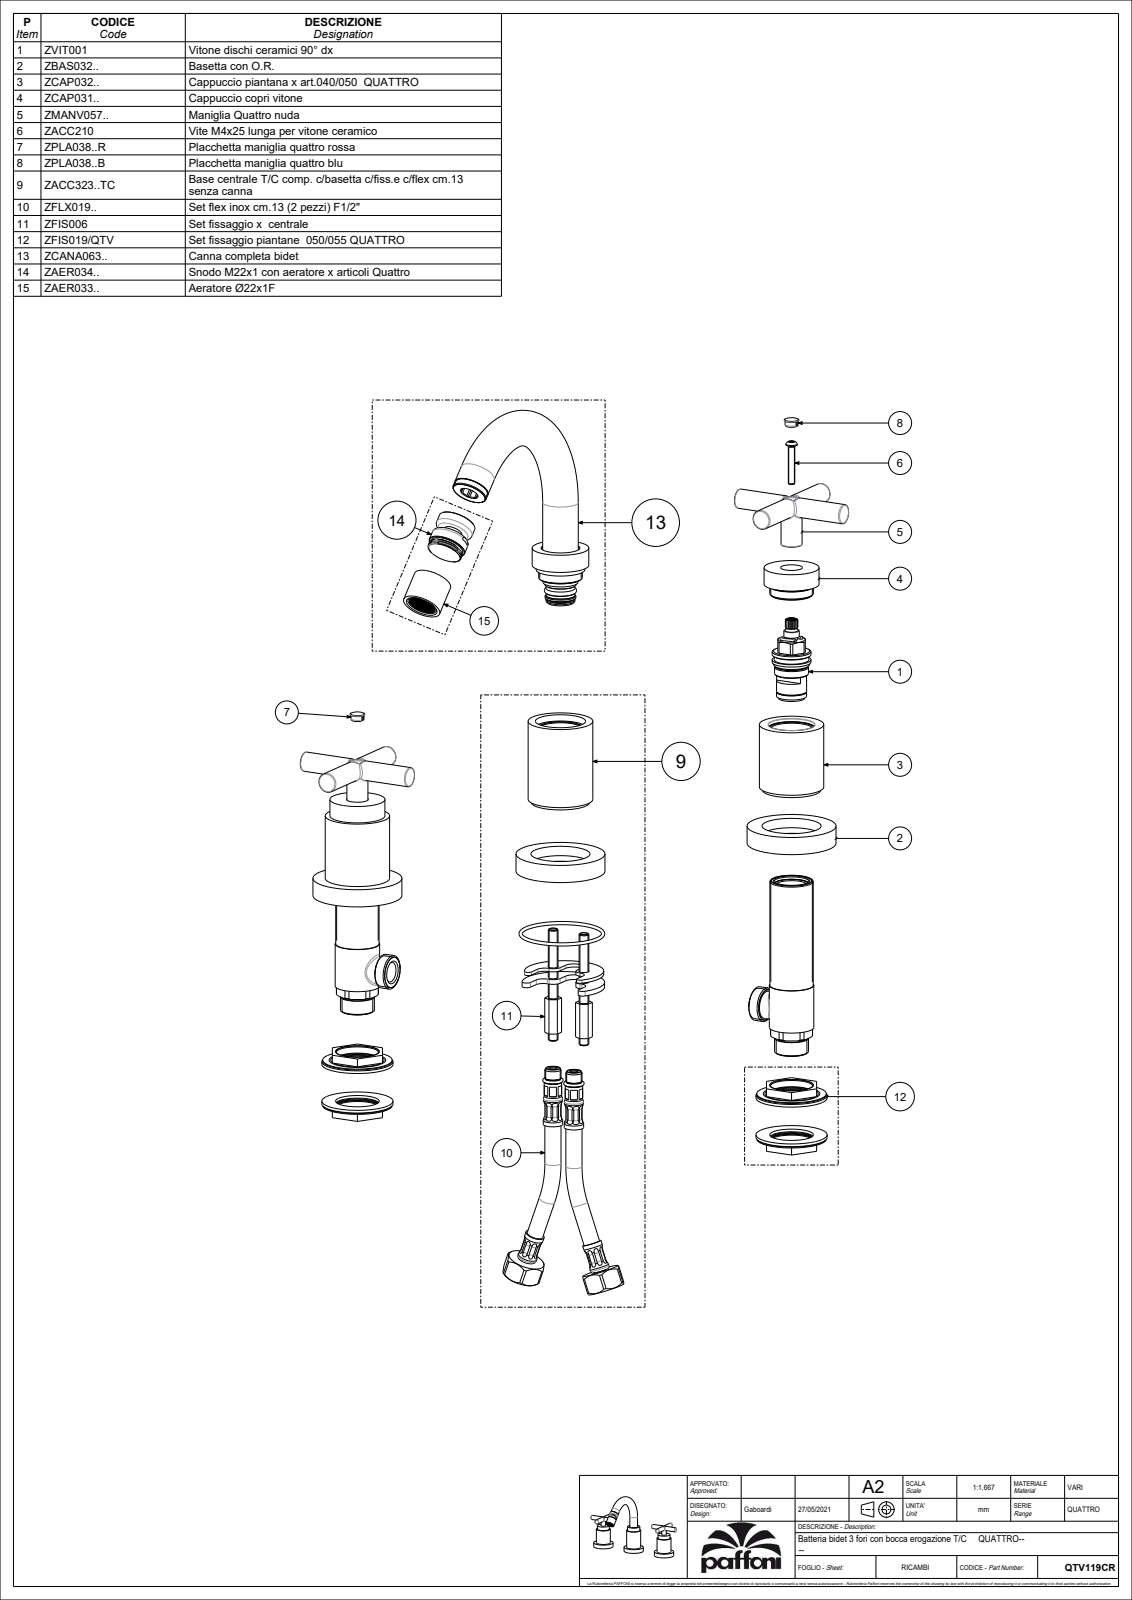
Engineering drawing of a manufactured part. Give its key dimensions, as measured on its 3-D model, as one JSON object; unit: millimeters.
{"part_name": "QTV119CR", "step_written_by": "CREO PARAMETRIC BY PTC INC, 2020044 (CONFIG_CONTROL_DESIGN)", "units": "millimeters", "bodies": {"solids": 8, "faces": 2566, "planar": 1968, "cylindrical": 350, "other": 248}, "overall_size": [275, 184.68, 172.12], "volume_mm3": 288613, "surface_area_mm2": 124077, "round_holes": [[19, 5], [4.5, 4], [7, 3], [25.5, 3], [36.5, 3], [47, 3], [53, 3], [3.3, 2], [5.25, 2], [8, 2], [8.8, 2], [9, 2]], "round_bosses_or_shafts": [[55, 3], [49, 3], [36, 3], [24, 3], [12, 3], [39.8, 2], [34, 2], [26.8, 2]], "partial_cylinders_radius": [[0.1, 34], [0.5, 4], [1, 4], [3, 2], [9.4, 2], [4.25, 1]], "face_to_face_distances": [11, 5, 6, 4, 10.5, 9, 2, 56.5, 50.5, 61.5], "hole_center_spacings": [9.01, 14.87, 15.4, 23.82, 89.56, 92.64, 100, 107.62]}
